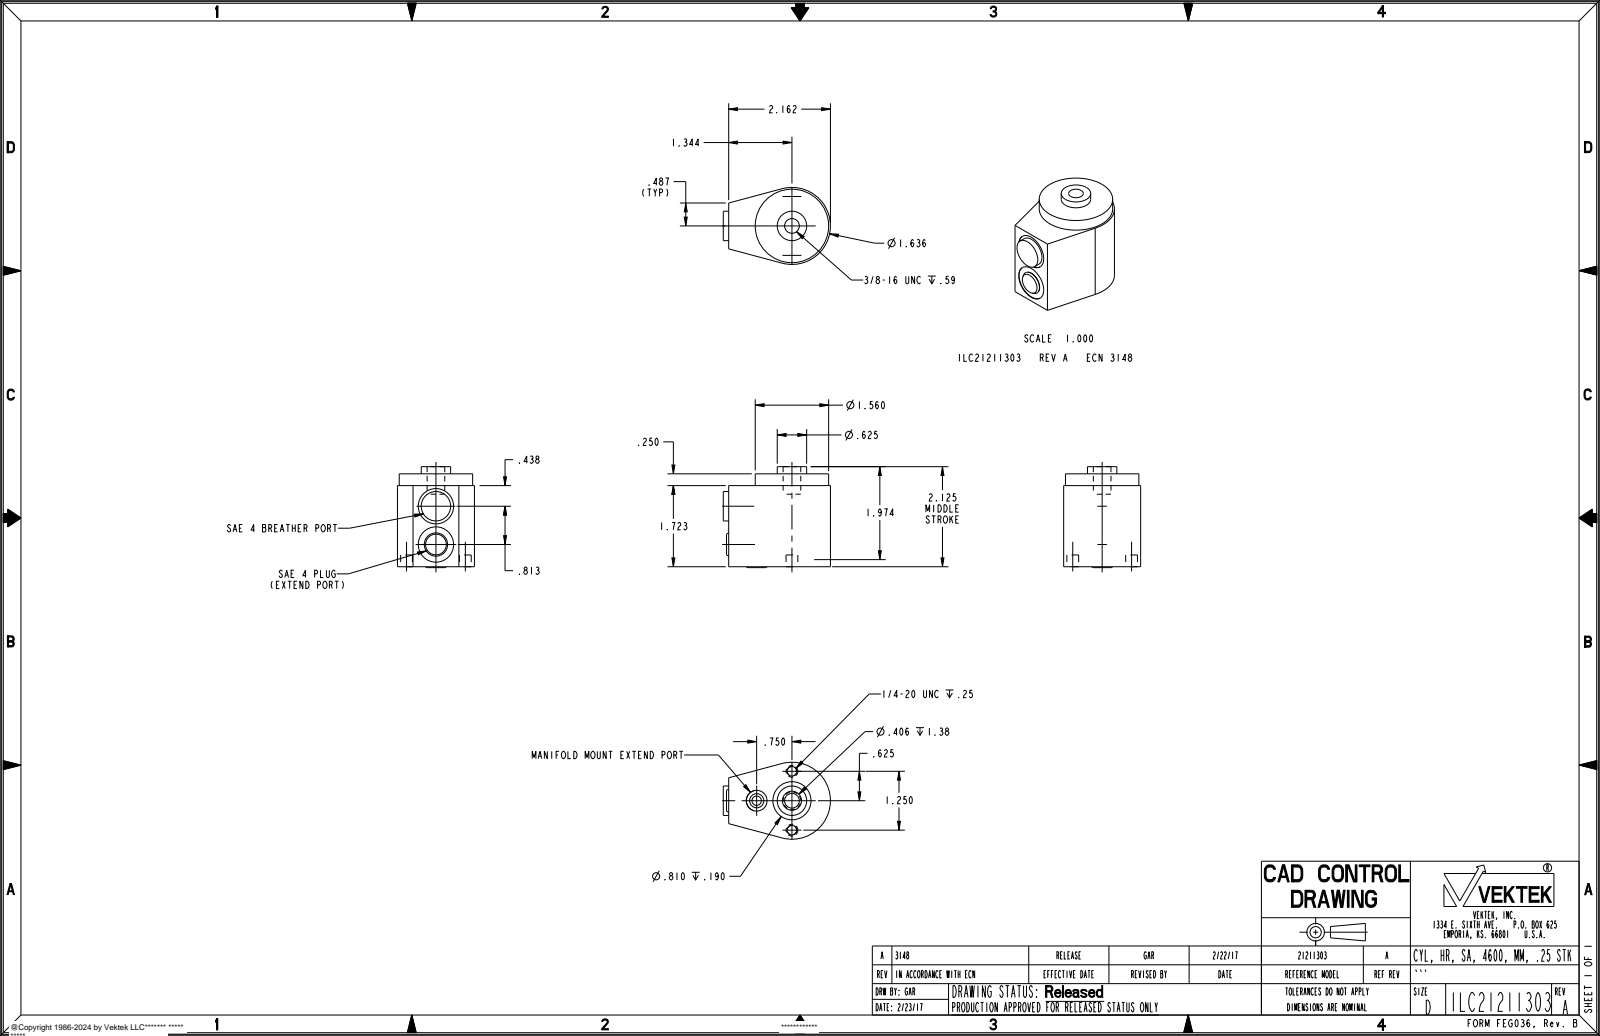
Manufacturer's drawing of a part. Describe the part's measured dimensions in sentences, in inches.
The part is named "ILC21211303". Its 3-D file was written by "PRO/ENGINEER BY PARAMETRIC TECHNOLOGY CORPORATION, 2013320 (AUTOMOTIVE_DESIGN)". It is 2 solids with 75 faces: 22 planar, 37 cylindrical and 16 other. Overall it measures 2.277 by 2.144 by 1.636 inches. Its volume is 4.932 cubic inches and its surface area 25.57 square inches. Round holes: 2 of diameter 0.204, 2 of diameter 0.392, 2 of diameter 0.75, 1 of diameter 0.199, 1 of diameter 0.313, 1 of diameter 0.406, 1 of diameter 0.441, 1 of diameter 0.81. Round bosses or shafts: 2 of diameter 0.625, 2 of diameter 0.25, 1 of diameter 1.56, 1 of diameter 0.375. Partial cylindrical surfaces (rounded edges, fillets, slot ends): 1 of radius 0.818. The main face-to-face distances are 1.973, 0.25, 1.723, 0.125, 0.115, 2.125, 0.402, 0.152, 0.19, 1.533. The hole center spacings are 0.625, 0.976, 0.75, 0.813, 1.25.
